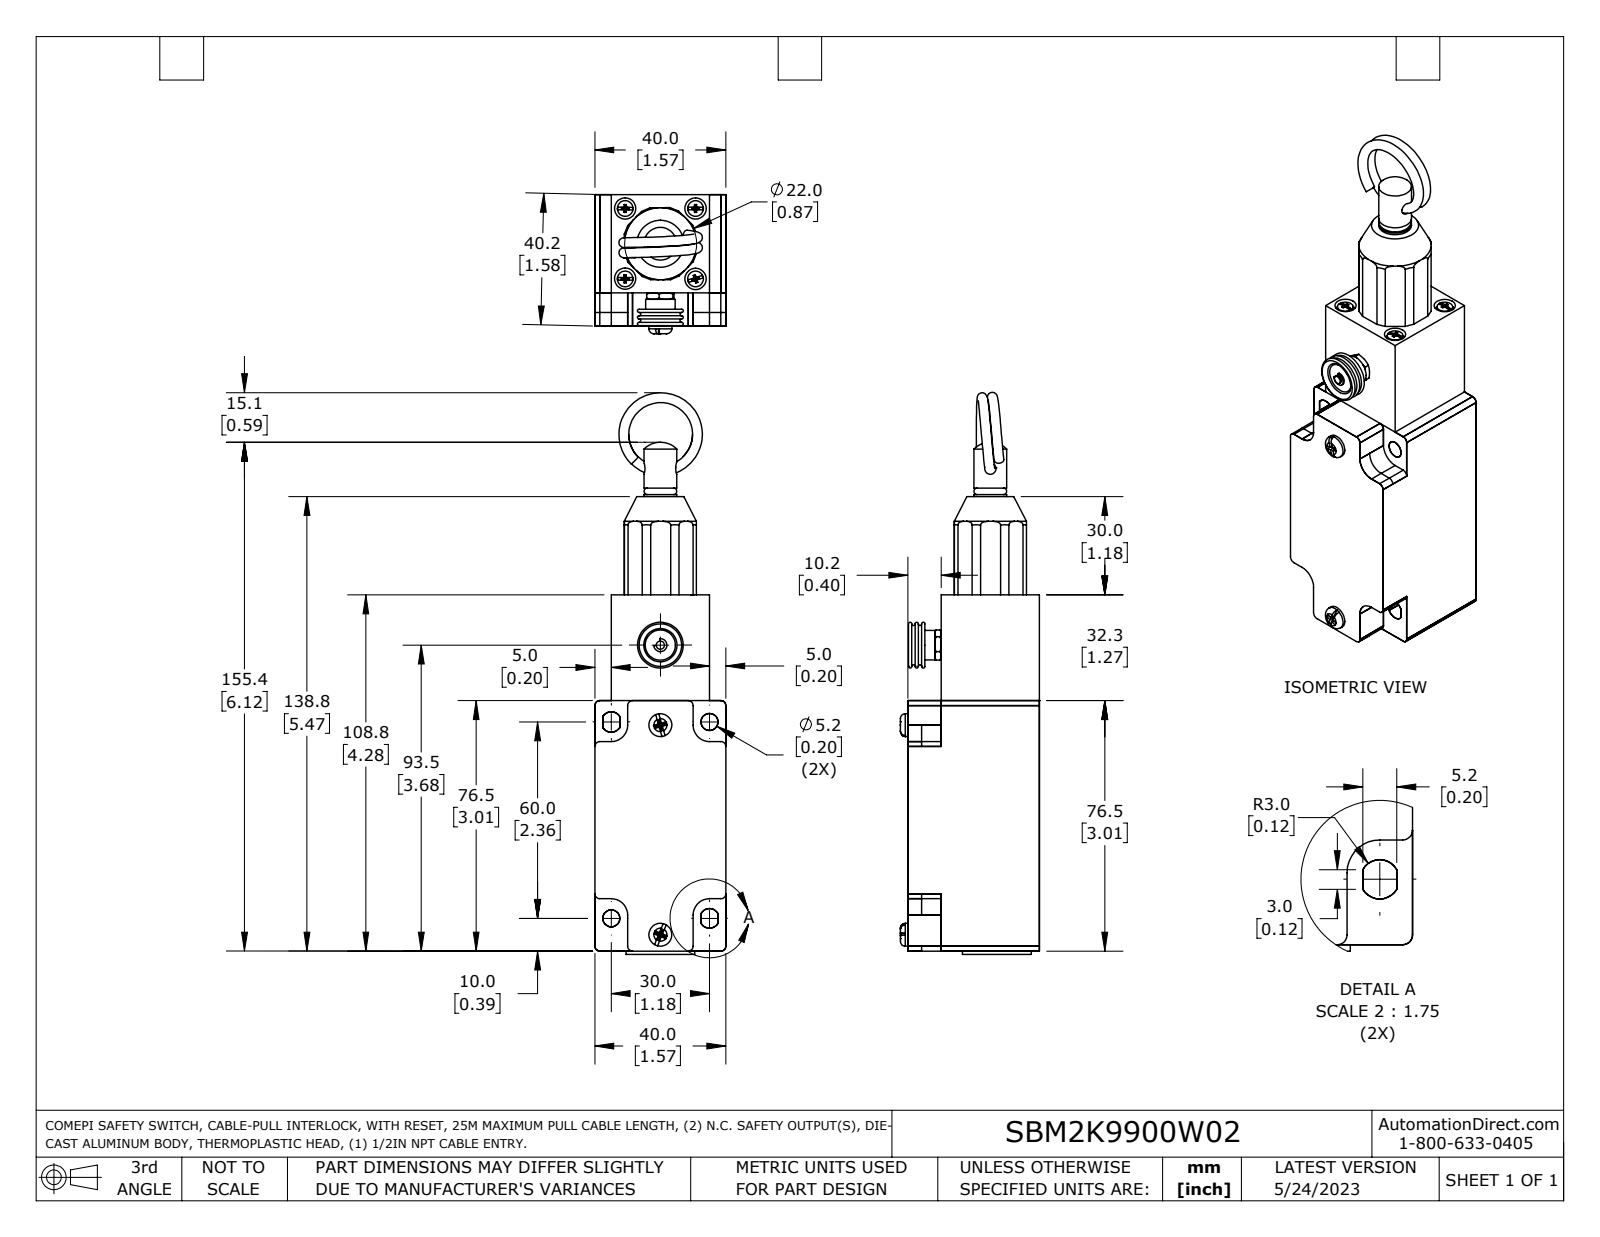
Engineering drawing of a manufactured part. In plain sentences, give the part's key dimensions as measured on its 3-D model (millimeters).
The part is named "SBM2K9900W02_REV2". Its 3-D file was written by "SolidWorks 2021 (AUTOMOTIVE_DESIGN)". It is 3 solids with 390 faces: 260 planar, 87 cylindrical and 43 other. Overall it measures 171.7 by 42.5 by 40 millimeters. Its volume is 286 100 cubic millimeters and its surface area 51 020 square millimeters. Round holes: 4 of diameter 3, 4 of diameter 6.5, 2 of diameter 3.3, 2 of diameter 5.2, 1 of diameter 3.5, 1 of diameter 18.5, 1 of diameter 22. Round bosses or shafts: 4 of diameter 4.8, 2 of diameter 7, 1 of diameter 21, 1 of diameter 10, 1 of diameter 9, 1 of diameter 6.3, 1 of diameter 2.5. Partial cylindrical surfaces (rounded edges, fillets, slot ends): 12 of radius 1.5, 4 of radius 5, 1 of radius 1, 1 of radius 2, 1 of radius 3, 1 of radius 3, 1 of radius 3.1, 1 of radius 3.1. The main face-to-face distances are 40, 30, 30, 5, 40.2, 40.2, 35, 5, 30, 10.2. The hole center spacings are 21.5, 15.2, 13.9, 16.7, 30.4, 2, 15, 15.1.
